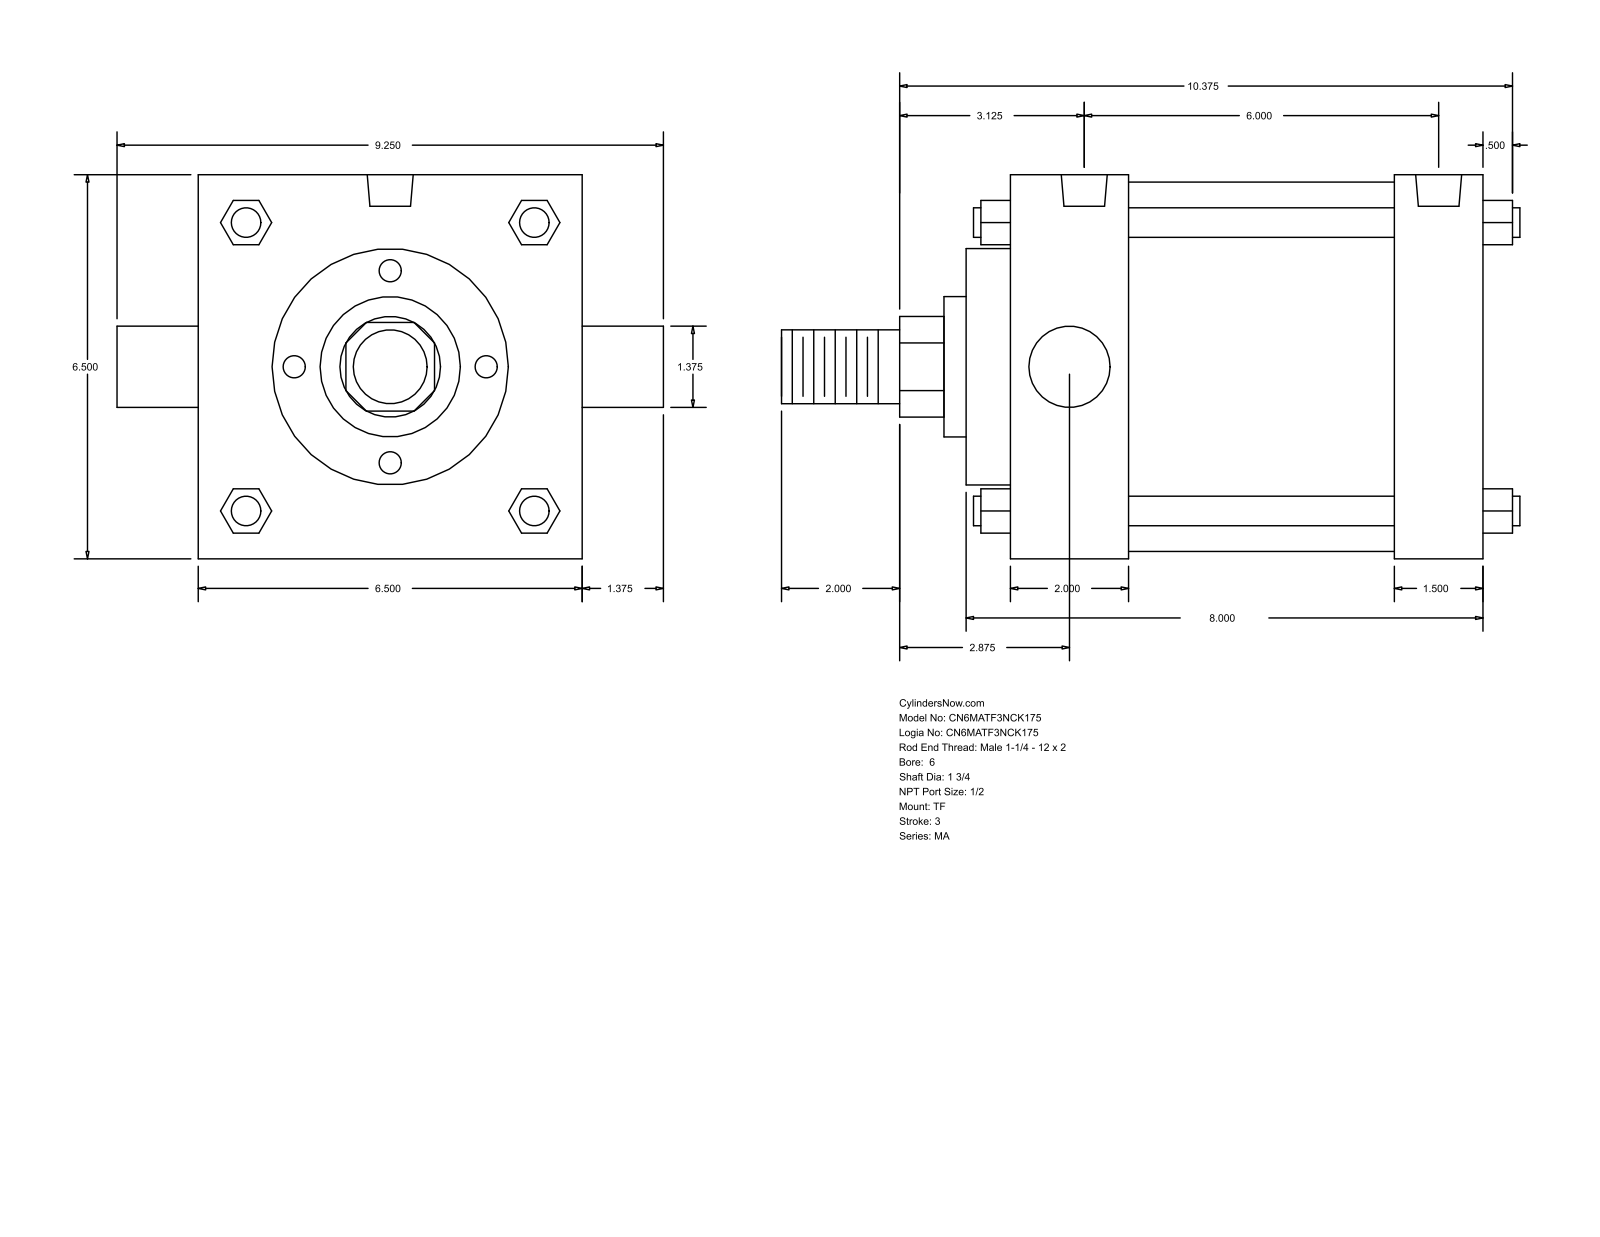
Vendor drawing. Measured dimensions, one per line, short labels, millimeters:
name: MA_TF__0600_1.75
written by: GSSL Pune (CONFIG_CONTROL_DESIGN)
unit: mm
bodies: 0 solids, 122 faces (93 planar, 29 cylindrical, 0 other)
size: 317.5 × 234.95 × 165.1
holes: 3× ⌀17.46, 2× ⌀19.77
bosses: 4× ⌀12.7, 1× ⌀158.75, 1× ⌀101.6, 1× ⌀60.33, 1× ⌀44.45, 1× ⌀34.92, 1× ⌀31.75
rounds: 1× R21.63
face distances: 165.1, 203.2, 19.05, 50.8, 38.1, 152.4, 114.3, 69.85, 184.15, 222.25
hole spacings: 152.4
